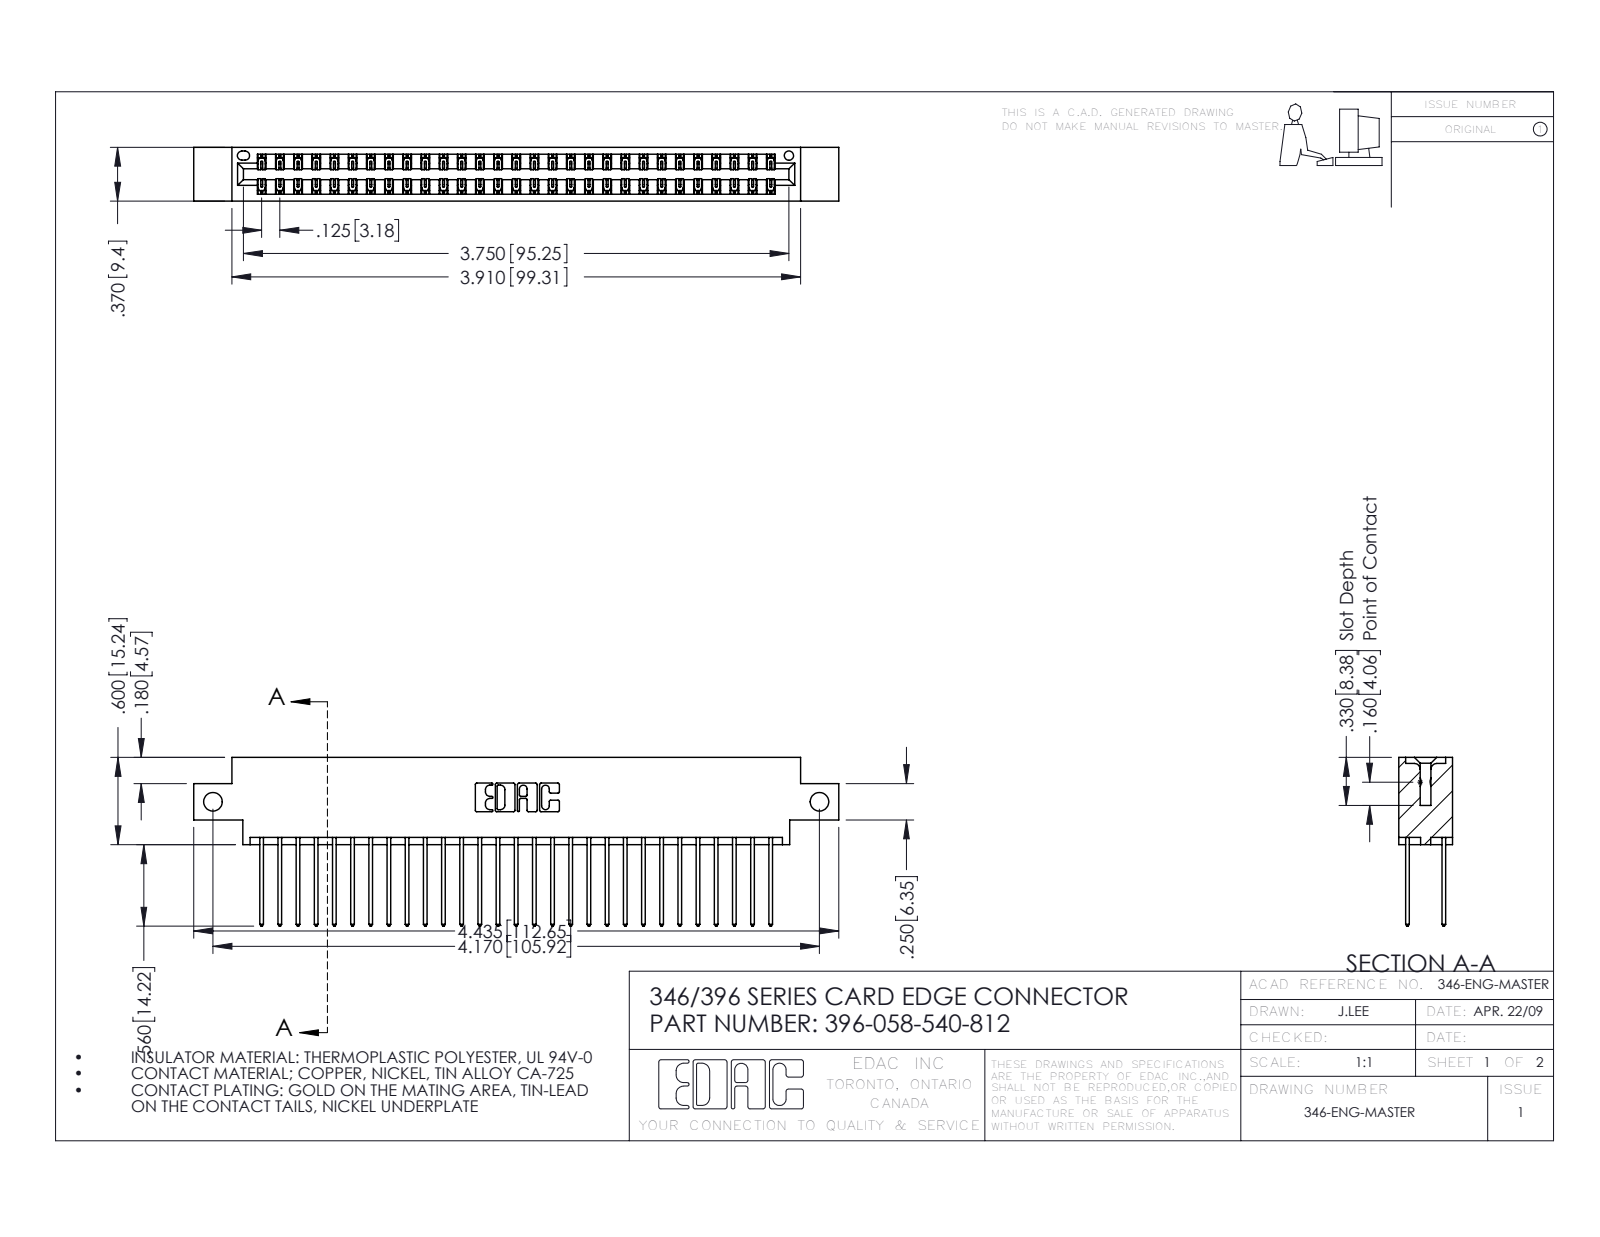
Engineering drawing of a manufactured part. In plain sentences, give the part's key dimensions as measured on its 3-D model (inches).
The part is named "346 Part_0.170 Offset - Side Mount; 396-058-540-812; 345-292-001_345-293-140". Its 3-D file was written by "SolidWorks 2016 (CONFIG_CONTROL_DESIGN)". It is 59 solids with 3142 faces: 2110 planar, 1032 cylindrical and 0 other. Overall it measures 4.435 by 1.16 by 0.37 inches. Its volume is 0.663 cubic inches and its surface area 24.5 square inches. Round holes: 2 of diameter 0.128, 1 of diameter 0.064. Partial cylindrical surfaces (rounded edges, fillets, slot ends): 87 of radius 0.006, 58 of radius 0.01, 22 of radius 0.01, 6 of radius 0.007, 6 of radius 0.031, 3 of radius 0.026, 2 of radius 0.014, 2 of radius 0.022. The main face-to-face distances are 0.048, 0.322, 0.25, 0.37, 0.072, 0.298, 0.025, 0.275, 0.148, 0.222. The hole center spacings are 4.17.
